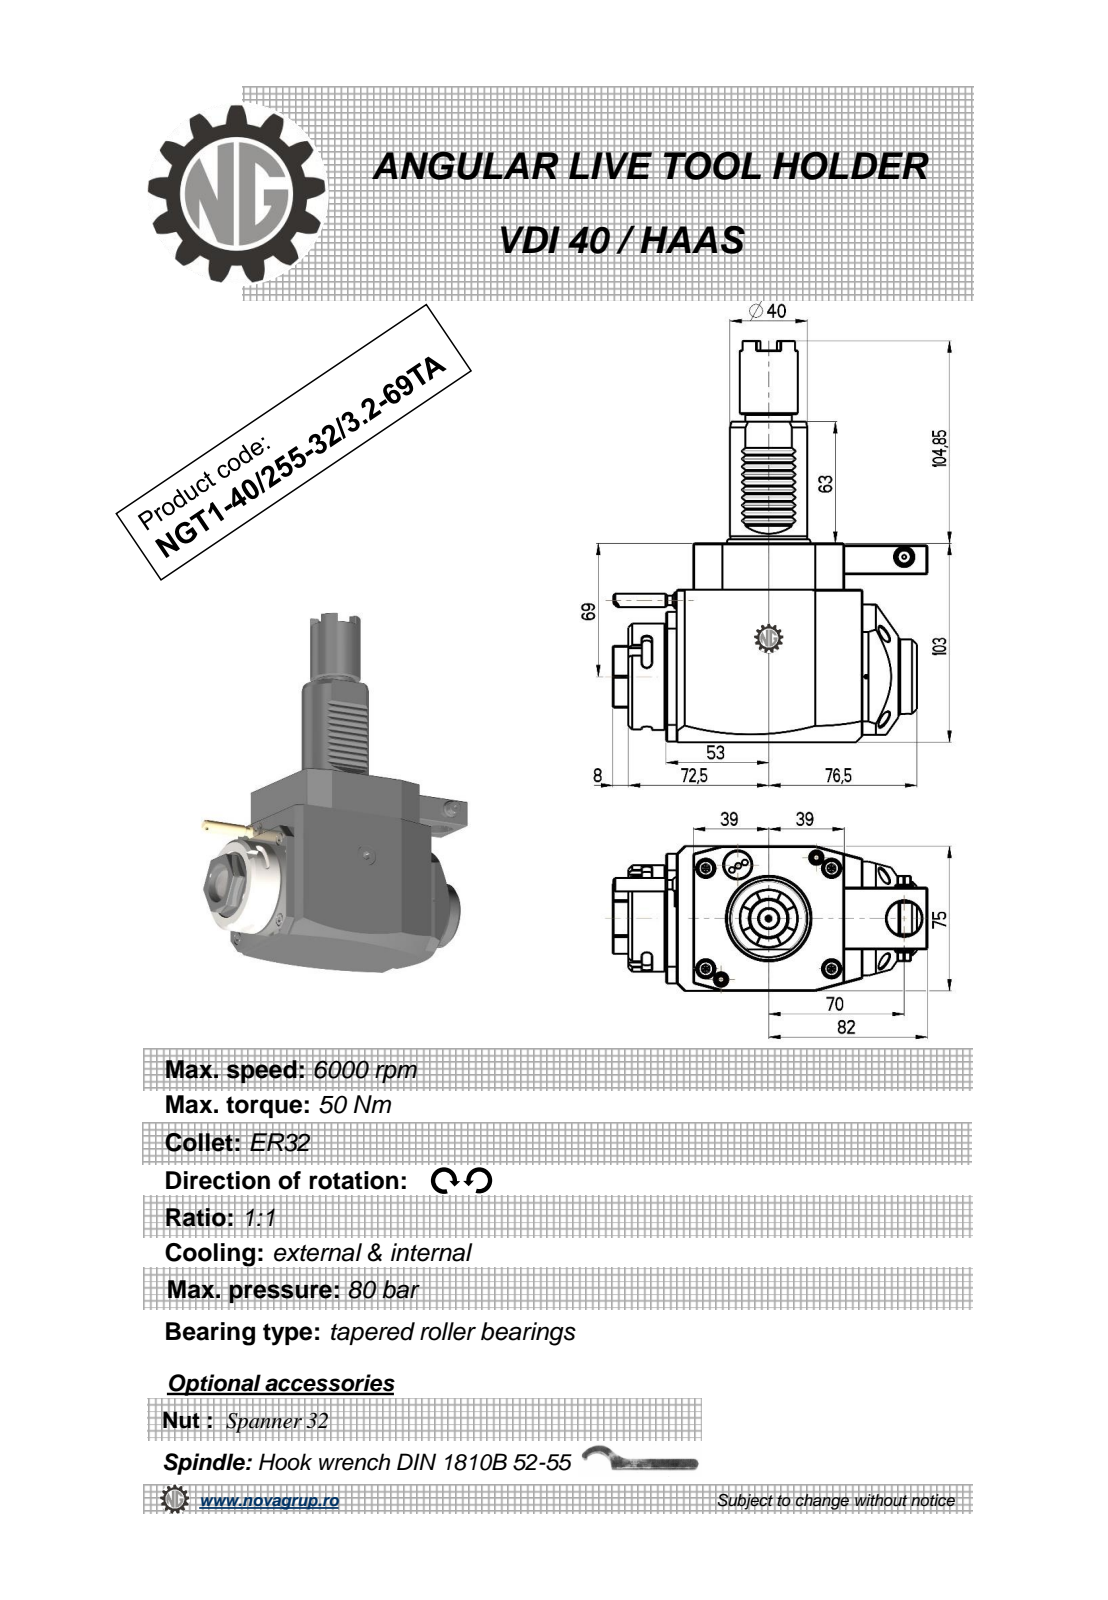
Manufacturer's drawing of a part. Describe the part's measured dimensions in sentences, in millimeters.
The part is named "NGT1_40_255_32_3_2_69TA". Its 3-D file was written by "PRO/ENGINEER BY PARAMETRIC TECHNOLOGY CORPORATION, 2010280 (CONFIG_CONTROL_DESIGN)". It is 1 solid with 397 faces: 219 planar, 88 cylindrical and 90 other. Overall it measures 207.85 by 162.5 by 75 millimeters. Its volume is 943 314 cubic millimeters and its surface area 75 207 square millimeters. Round holes: 1 of diameter 2, 1 of diameter 2.5, 1 of diameter 3, 1 of diameter 9.5, 1 of diameter 18, 1 of diameter 20, 1 of diameter 23. Round bosses or shafts: 2 of diameter 8.96, 1 of diameter 55, 1 of diameter 48, 1 of diameter 40, 1 of diameter 38.5, 1 of diameter 30, 1 of diameter 24, 1 of diameter 10. Partial cylindrical surfaces (rounded edges, fillets, slot ends): 10 of radius 0.3, 6 of radius 2.5, 2 of radius 180, 1 of radius 0.5, 1 of radius 3.85, 1 of radius 4.25, 1 of radius 24.5, 1 of radius 37.5. The main face-to-face distances are 75, 103, 33.5, 19.5, 79, 8, 14, 102, 21.5, 87. The hole center spacings are 28.11, 43.2, 61.5, 70.
